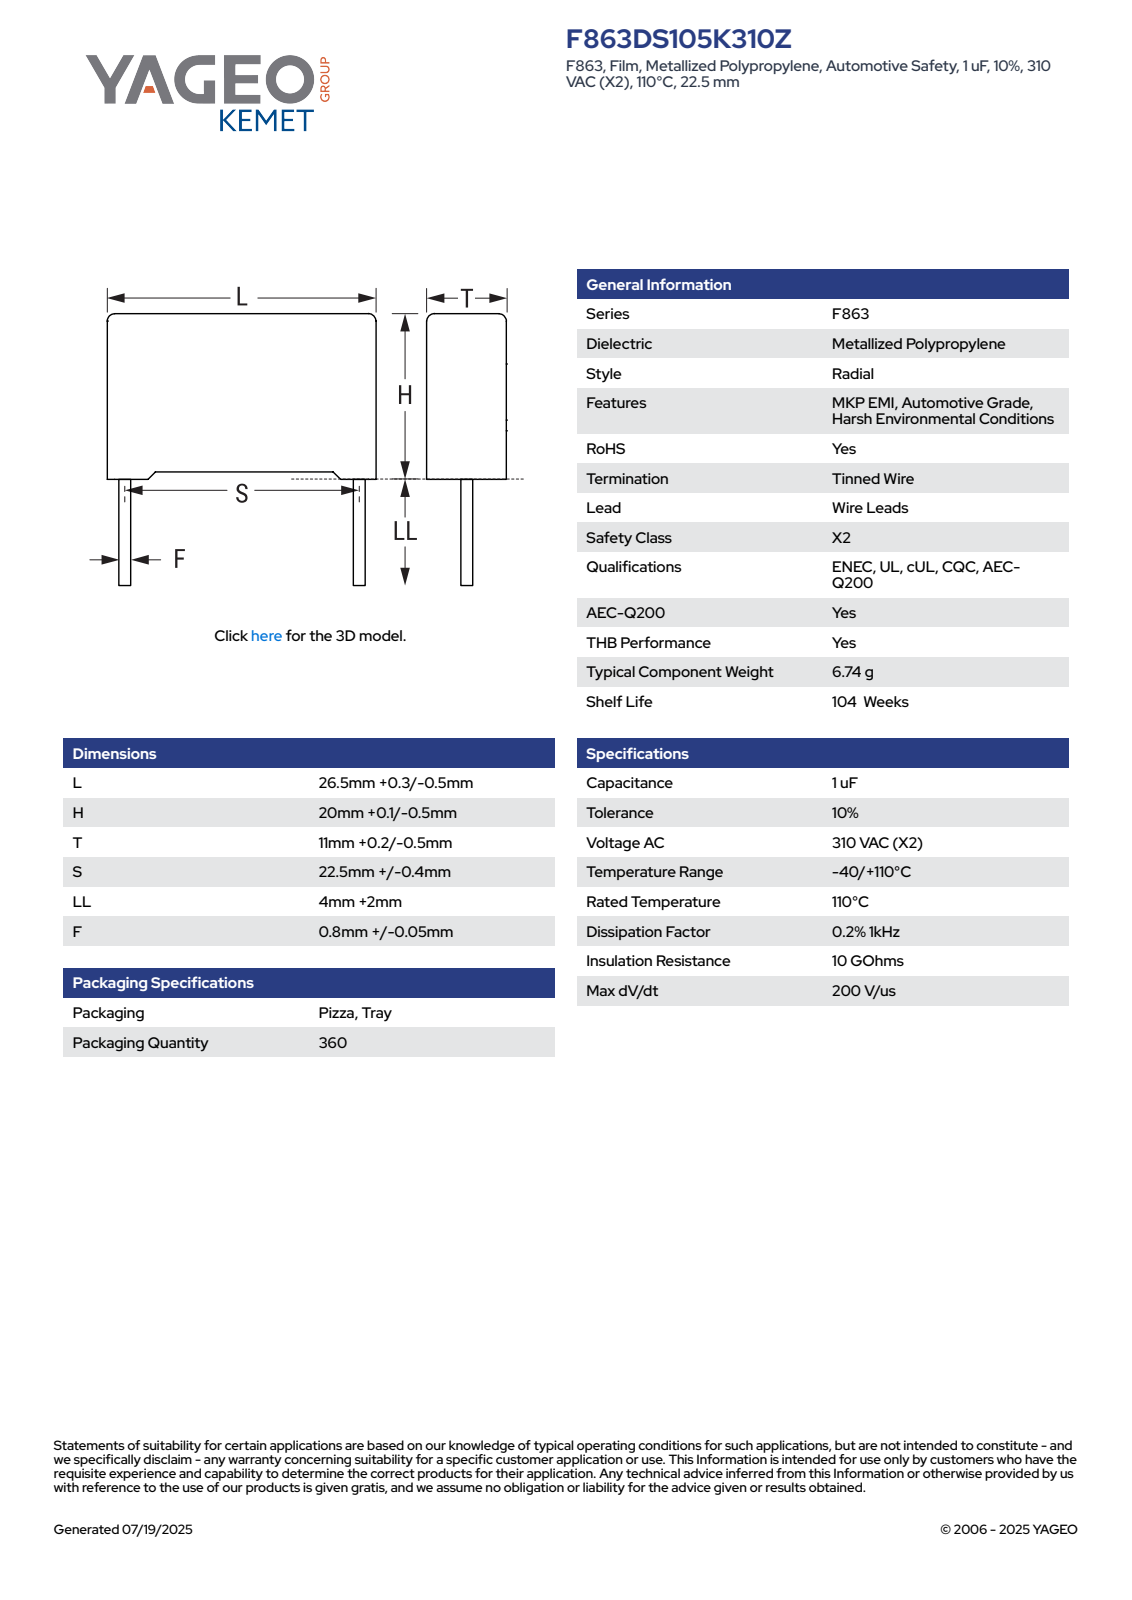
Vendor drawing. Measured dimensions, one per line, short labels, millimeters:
name: CFR_RB_26.5X20X11_L26.8H20.1T11.2S22.5LL6F0.85
written by: SolidWorks 2014 (AUTOMOTIVE_DESIGN)
unit: mm
bodies: 4 solids, 89 faces (81 planar, 8 cylindrical, 0 other)
size: 26.8 × 26.1 × 11.21
volume: 5 769 mm³; area: 2 153 mm²
bosses: 2× ⌀0.85
rounds: 4× R0.72
face distances: 11.2, 19.2, 26.8, 11.21, 10.6, 0.6, 0.9, 20.1, 10.61, 0.61
